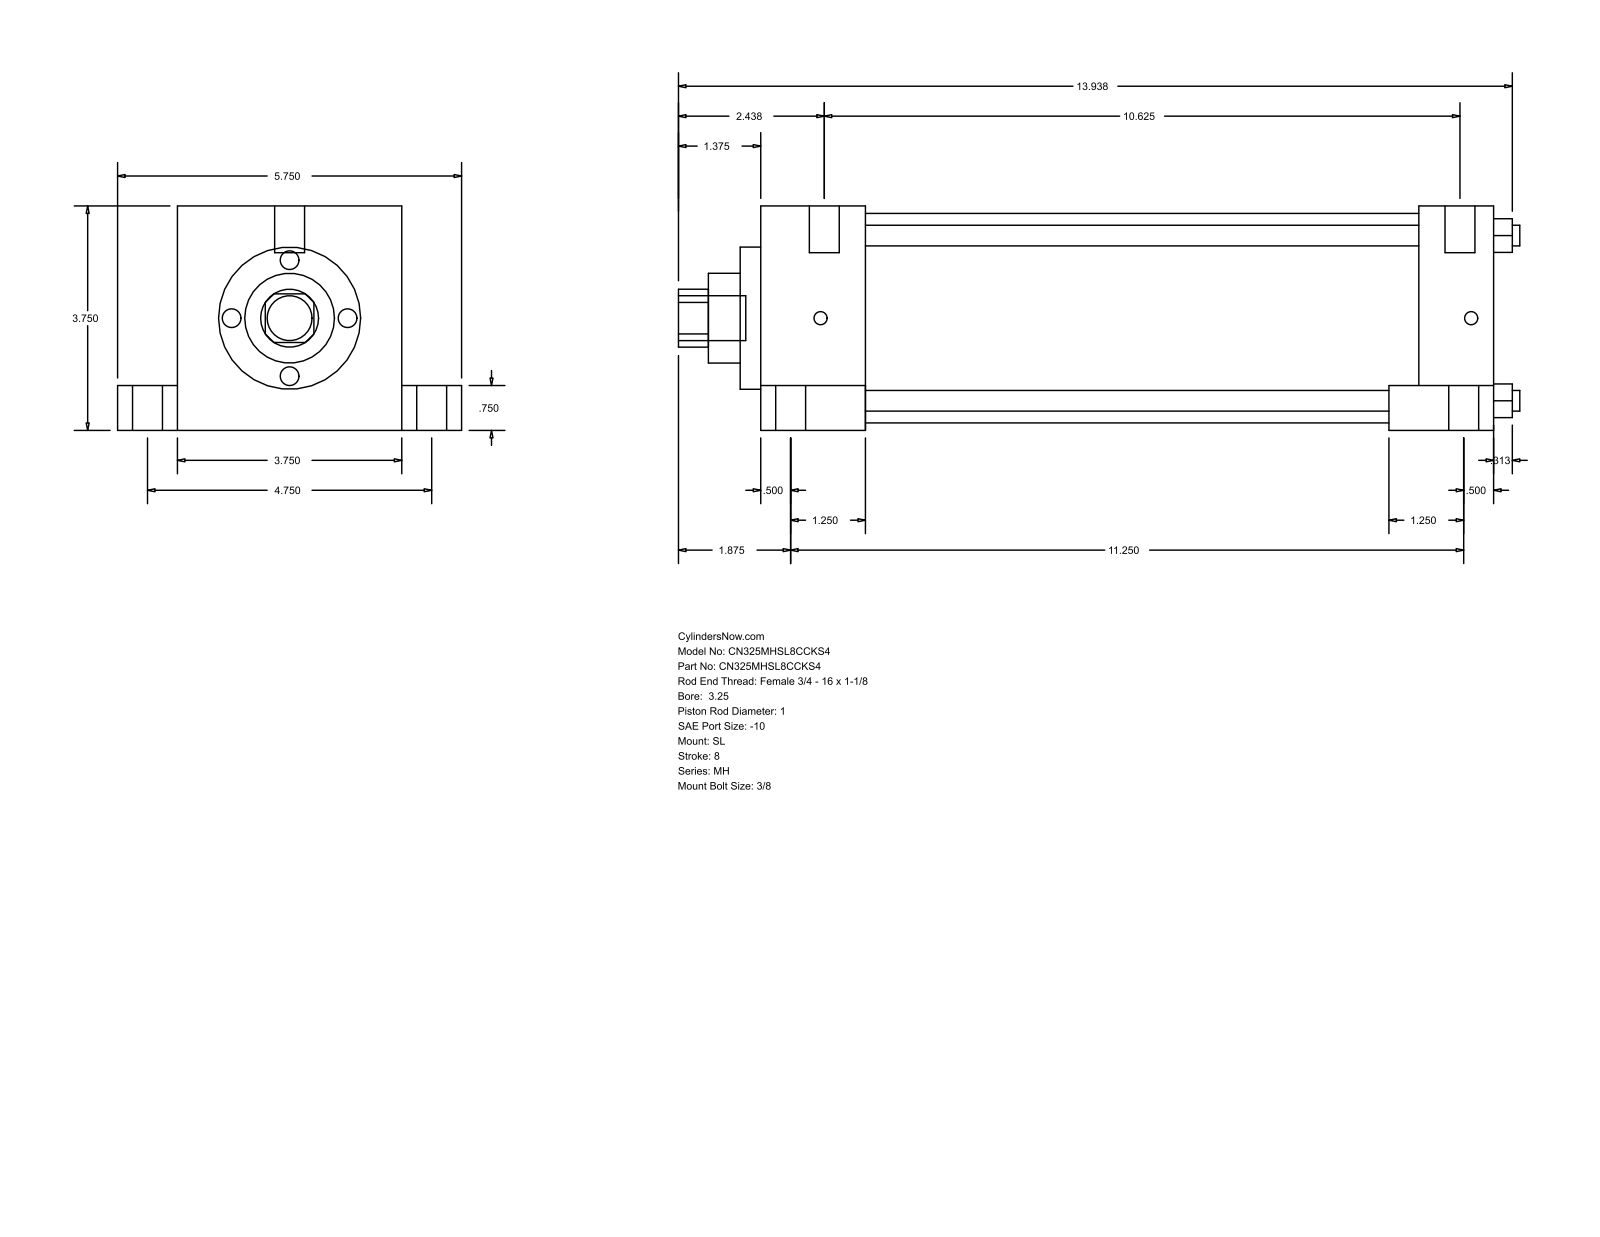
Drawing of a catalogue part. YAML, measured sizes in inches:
part_name: "MH_SL__0325_1"
step_written_by: "GSSL Pune (CONFIG_CONTROL_DESIGN)"
units: inches
bodies: {solids: 0, faces: 110, planar: 77, cylindrical: 33, other: 0}
overall_size: [14.063, 5.75, 3.75]
round_holes:
  - {diameter: 0.345, count: 4}
  - {diameter: 1, count: 1}
  - {diameter: 1.5, count: 1}
  - {diameter: 2.375, count: 1}
  - {diameter: 3.5, count: 1}
round_bosses_or_shafts:
  - {diameter: 0.5, count: 6}
  - {diameter: 0.75, count: 5}
  - {diameter: 0.219, count: 4}
partial_cylinders:
  - {radius: 0.484, count: 1}
face_to_face_distances: [3.75, 12.25, 1.75, 10.5, 1, 4.75, 0.75, 3, 11, 9.25]
hole_center_spacings: [1.952, 2.76, 3.903]
